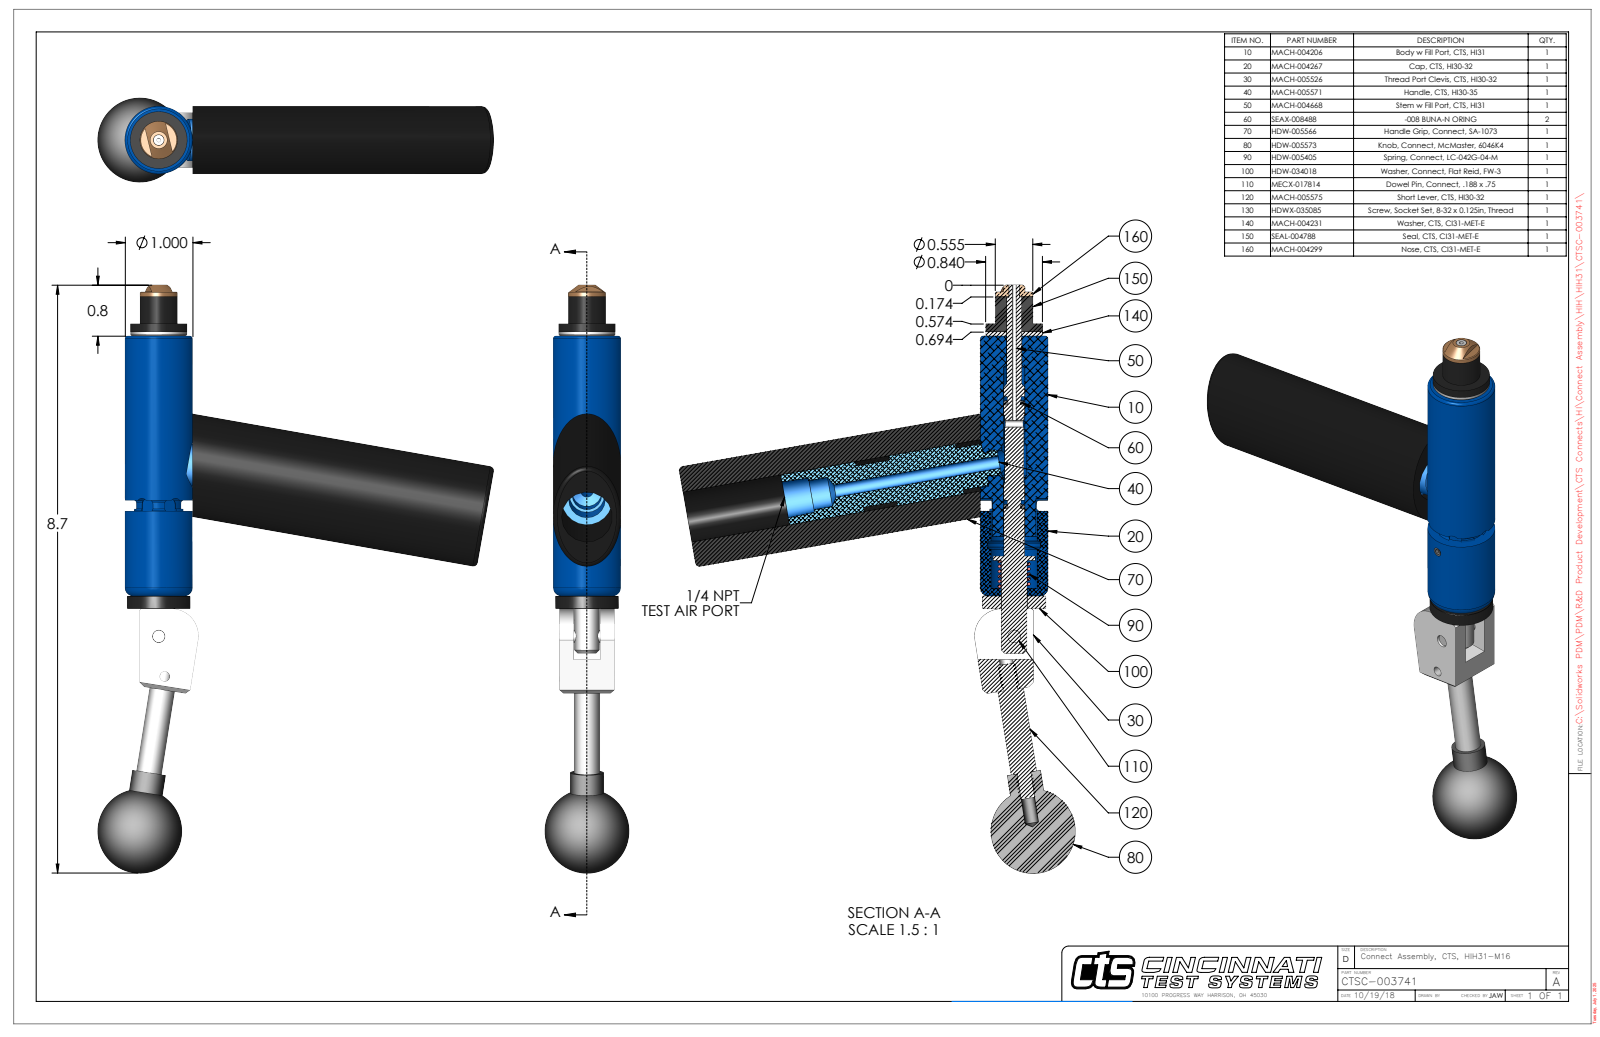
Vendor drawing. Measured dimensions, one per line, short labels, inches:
name: CTSC-003741
written by: SolidWorks 2023 (AUTOMOTIVE_DESIGN)
unit: in
bodies: 10 solids, 317 faces (117 planar, 131 cylindrical, 69 other)
size: 8.692 × 5.856 × 1.25
volume: 9.367 in³; area: 76.67 in²
holes: 2× ⌀0.201, 1× ⌀0.063, 1× ⌀0.109, 1× ⌀0.136, 1× ⌀0.15, 1× ⌀0.159, 1× ⌀0.187, 1× ⌀0.189, 1× ⌀0.218, 1× ⌀0.228, 1× ⌀0.229, 1× ⌀0.385
bosses: 1× ⌀1, 1× ⌀0.936, 1× ⌀0.84, 1× ⌀0.837, 1× ⌀0.75, 1× ⌀0.62, 1× ⌀0.555, 1× ⌀0.555
rounds: 6× R0.093, 2× R0.029, 1× R0.067, 1× R0.325, 1× R0.375, 1× R0.4, 1× R0.454
face distances: 0.21, 0.602, 0.06, 3.9, 3.841, 0.812, 4.088, 4.028, 0.187, 0.391
hole spacings: 0.599, 1.658, 2.252
